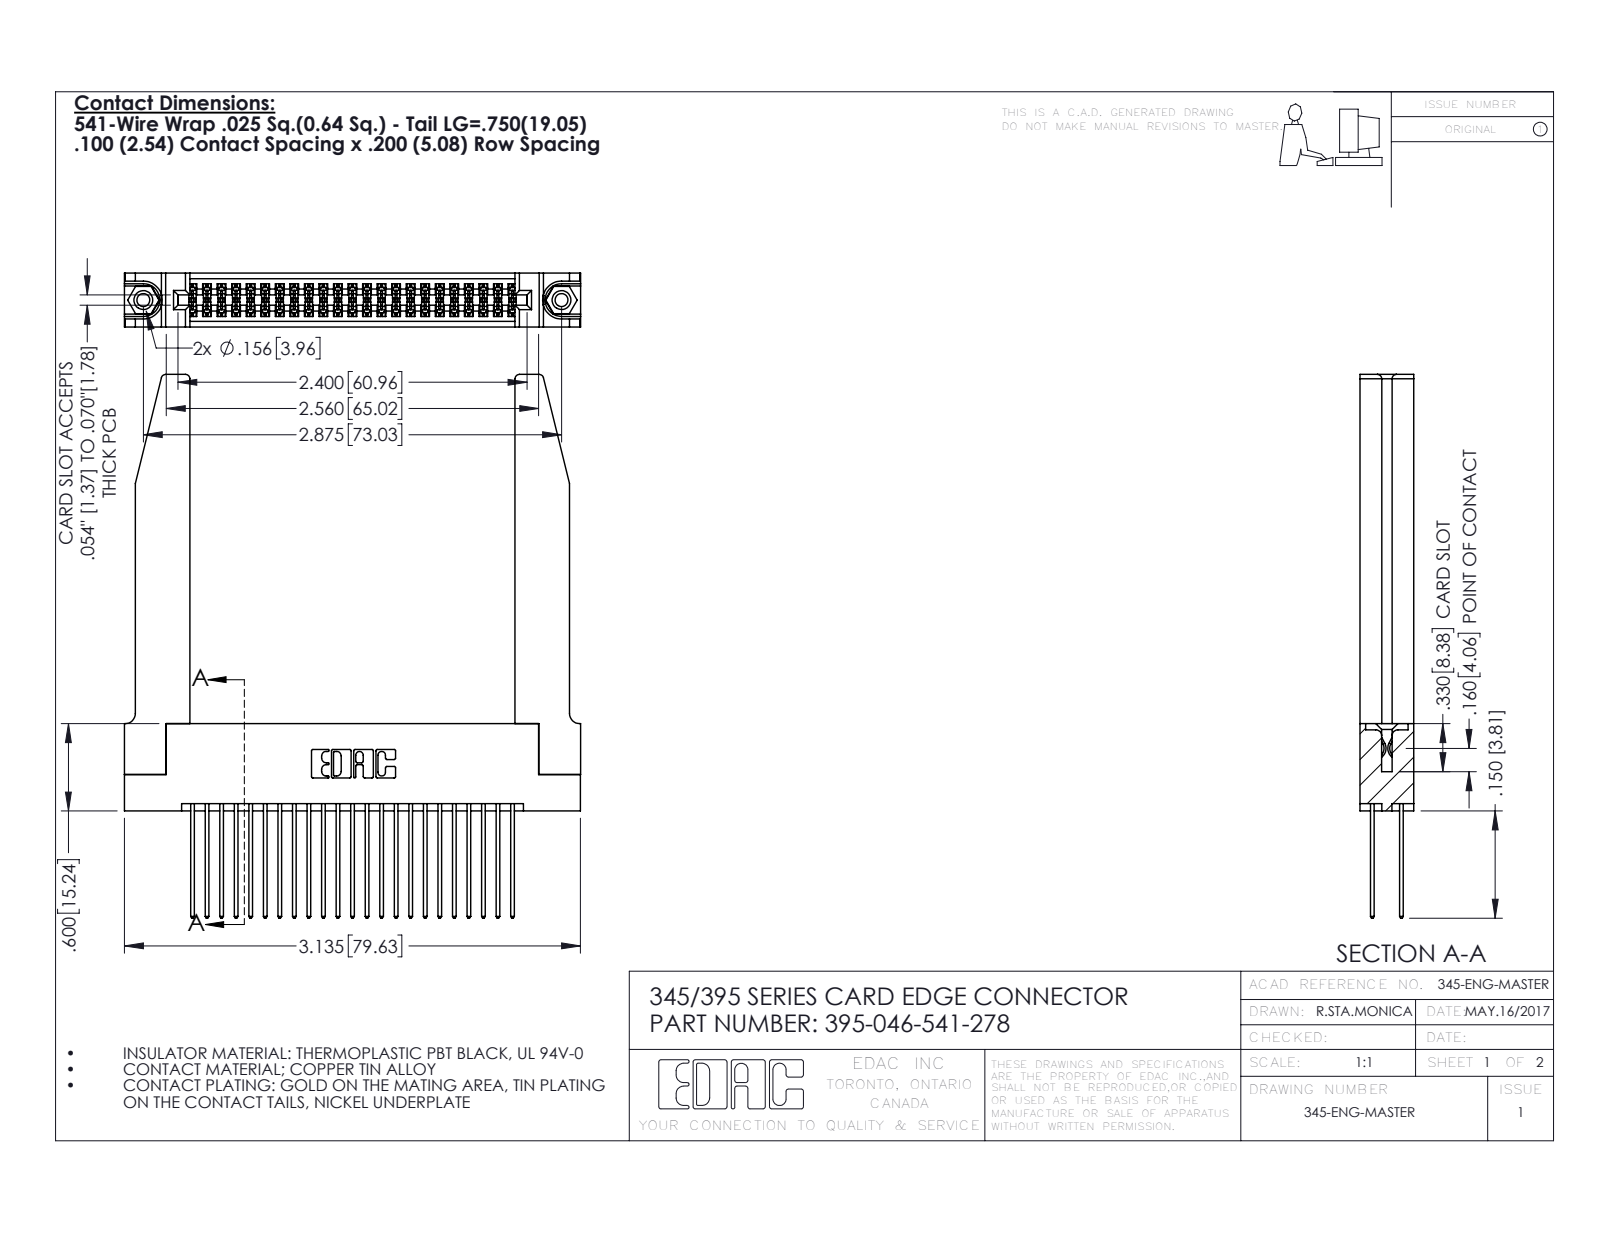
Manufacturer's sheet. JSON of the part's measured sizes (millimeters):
{"part_name": "395-046-541-278; 345 Part_Flush Mounting Lugs - 0.156 Dia-TH; 345-292-001_345-293-141; 345-220-078_345-220-078 (+1 more)", "step_written_by": "SolidWorks 2016 (CONFIG_CONTROL_DESIGN)", "units": "millimeters", "bodies": {"solids": 51, "faces": 2660, "planar": 1740, "cylindrical": 868, "other": 52}, "overall_size": [94.9, 79.7, 9.4], "volume_mm3": 15600, "surface_area_mm2": 19280, "round_holes": [[2.3, 2], [3.2, 2], [4, 2], [1.6, 1]], "round_bosses_or_shafts": [[3.9, 2]], "partial_cylinders_radius": [[0.2, 69], [0.3, 46], [0.3, 22], [0.8, 8], [0.2, 6], [0.8, 6], [0.7, 3], [0.4, 2]], "face_to_face_distances": [9.4, 1.8, 7.6, 5.1, 2.5, 6.9, 0.6, 5.7, 4.4, 3.8], "hole_center_spacings": [6.9, 67.1, 73]}
